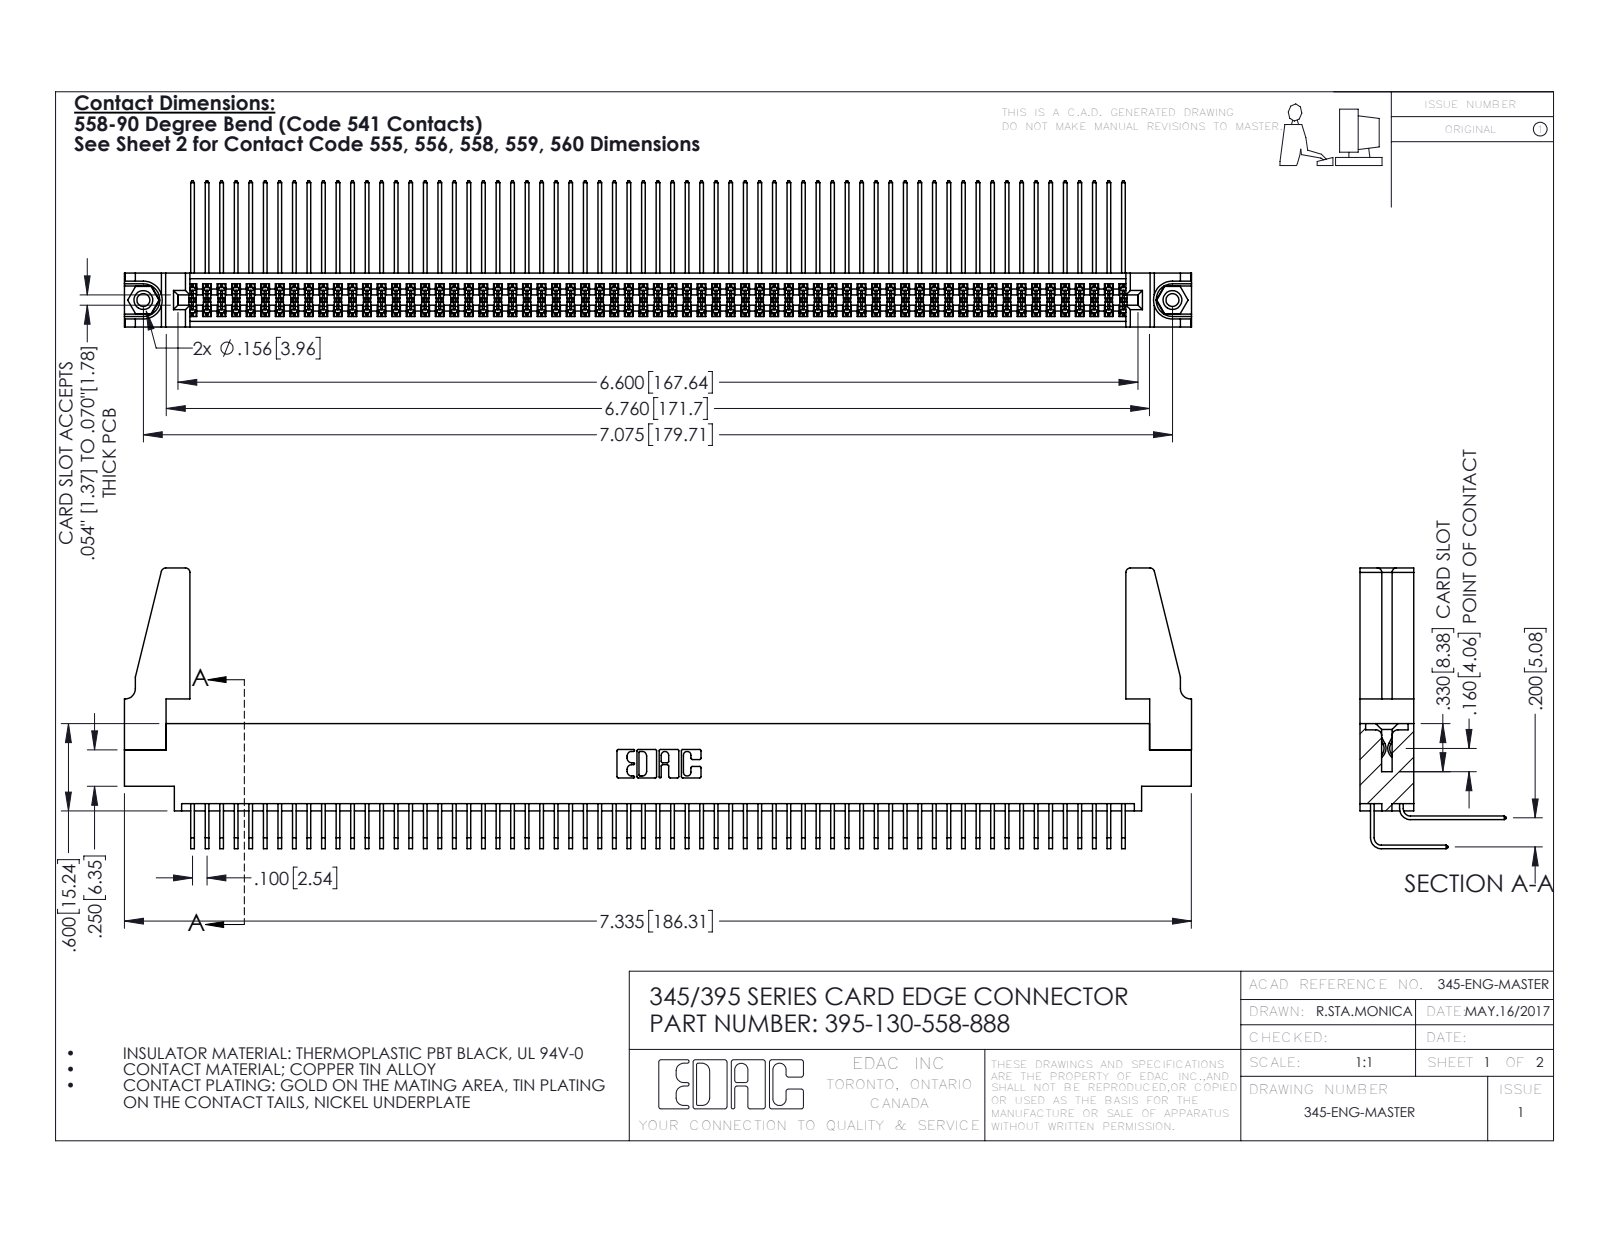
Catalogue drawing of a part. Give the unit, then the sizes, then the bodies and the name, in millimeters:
Units: millimetres
Overall size (bounding box): 186.3 × 49 × 25.5
Round holes (diameter × count): ⌀2.3 ×2, ⌀3.2 ×2, ⌀4 ×2, ⌀1.6 ×1
Round bosses / shafts (diameter × count): ⌀3.9 ×2
Partial cylindrical surfaces — rounded edges, fillets, slot ends (radius × count): R0.2 ×196, R0.3 ×22, R0.8 ×8, R0.2 ×6, R0.8 ×6, R0.7 ×3, R0.4 ×2, R0.5 ×2
Main face-to-face distances: 1.8, 7.6, 5.1, 9.4, 2.5, 6.9, 0.6, 5.7, 4.4, 0.6
Hole centre spacings: 6.9, 173.7, 179.7
Volume: 22 200 mm³ · Surface area: 35 250 mm²
Bodies: 135 solids, 7014 faces (4706 planar, 2292 cylindrical, 16 other)
Part name (STEP PRODUCT): 345-292-001_558 Tail - 2; 345 Part_0.170 Offset - 0.156 Dia-TH; 395-130-558-888; 345-250-001_345-250-001-102 (+2 more)
STEP written by: SolidWorks 2016 (CONFIG_CONTROL_DESIGN)
